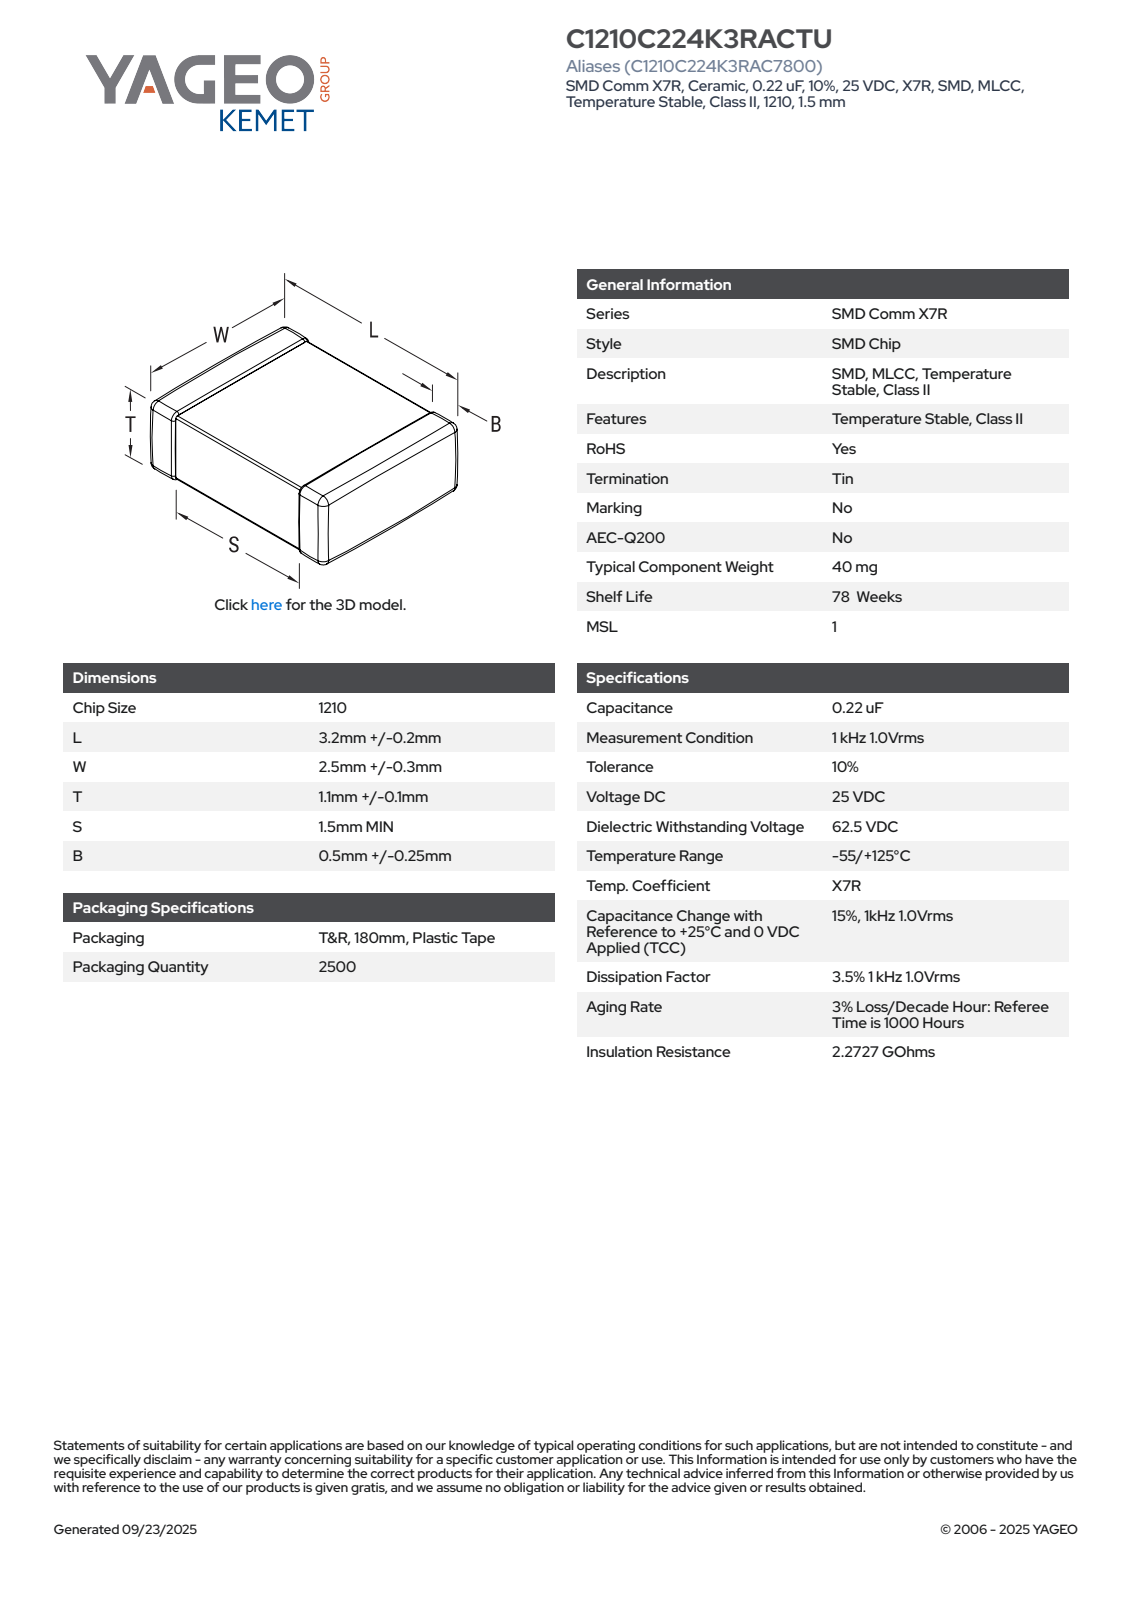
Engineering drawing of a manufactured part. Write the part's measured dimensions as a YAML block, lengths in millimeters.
part_name: "CCS_CCSTDNOS_1210_L3.4W2.8T1.2B0.75"
step_written_by: "SolidWorks 2021 (AUTOMOTIVE_DESIGN)"
units: millimeters
bodies: {solids: 4, faces: 125, planar: 71, cylindrical: 38, other: 16}
overall_size: [3.4, 2.8, 1.2]
volume: 11
surface_area: 33
face_to_face_distances: [1.14, 1.08, 1.2, 3.4, 2.74, 2.68, 2.8, 1.15, 1.09, 1.3]
